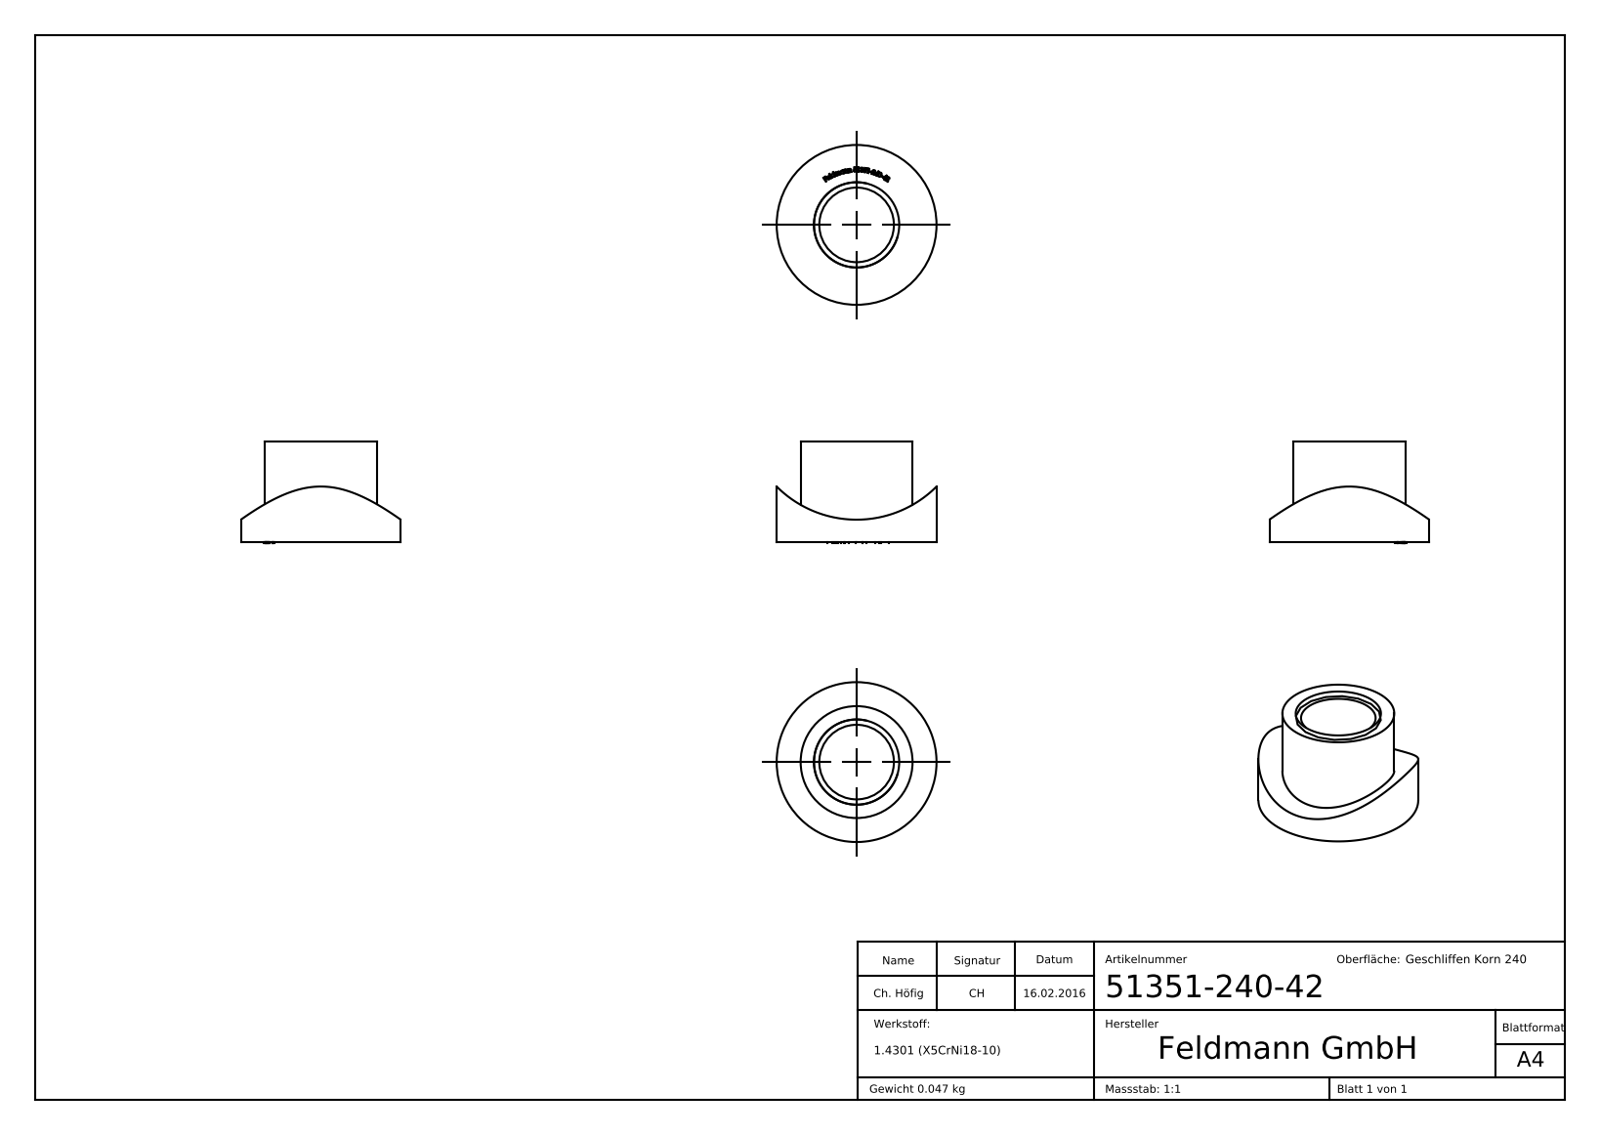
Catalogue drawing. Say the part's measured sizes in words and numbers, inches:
The part is named "51351-240-42". Its 3-D file was written by "SolidWorks 2015 (CONFIG_CONTROL_DESIGN)". It is 1 solid with 265 faces: 155 planar, 7 cylindrical and 103 other. Overall it measures 1.181 by 1.181 by 0.748 inches. Its volume is 0.362 cubic inches and its surface area 5.437 square inches. Round holes: 1 of diameter 0.551. Round bosses or shafts: 1 of diameter 1.181, 1 of diameter 0.827. Partial cylindrical surfaces (rounded edges, fillets, slot ends): 1 of radius 0.835. The main face-to-face distances are 0.748, 0.744, 0.013, 0.016, 0.017, 0.017, 0.015, 0.034, 0.031, 0.031.
